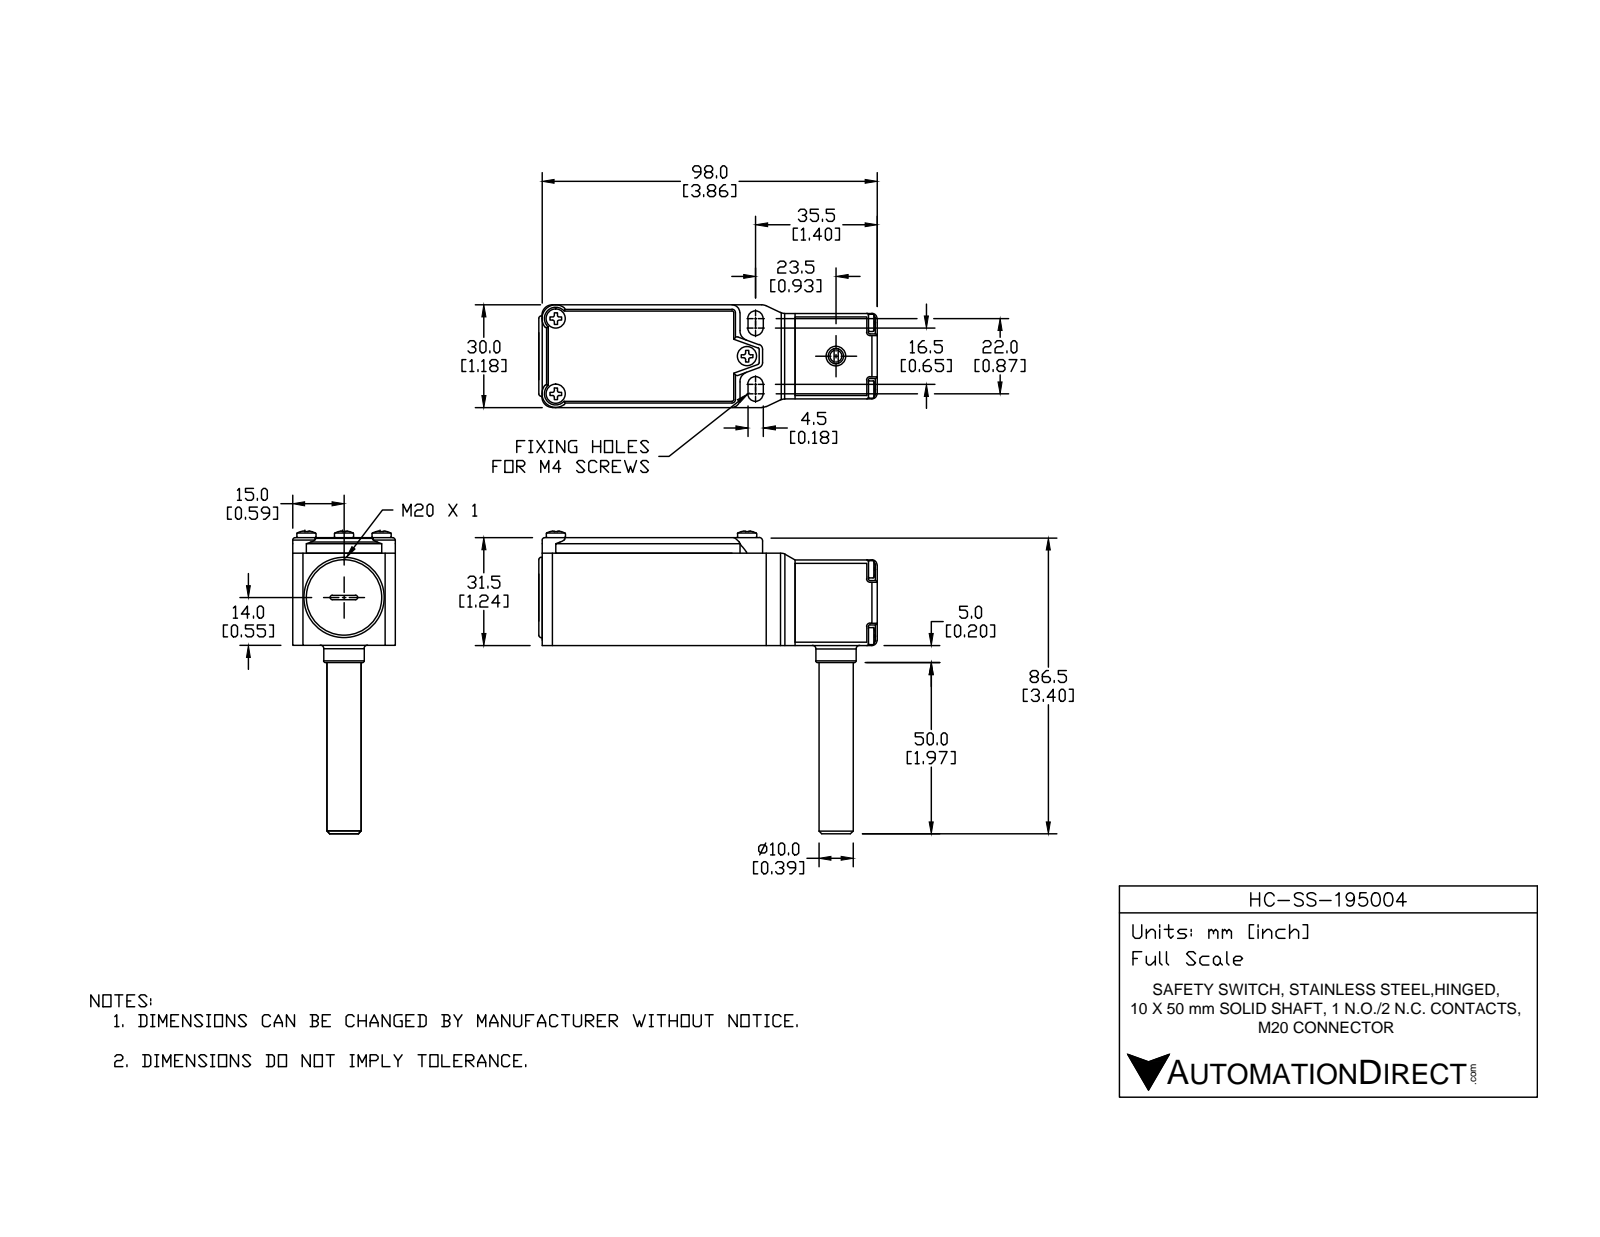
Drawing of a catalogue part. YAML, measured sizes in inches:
part_name: "HC-SS-195004"
step_written_by: "SolidWorks 2014 (AUTOMOTIVE_DESIGN)"
units: inches
bodies: {solids: 13, faces: 1168, planar: 347, cylindrical: 466, other: 355}
overall_size: [3.898, 3.482, 1.181]
volume: 2.649
surface_area: 52.99
round_holes:
  - {diameter: 0.098, count: 8}
  - {diameter: 0.126, count: 7}
  - {diameter: 0.157, count: 3}
  - {diameter: 0.059, count: 2}
  - {diameter: 0.071, count: 2}
  - {diameter: 0.087, count: 2}
  - {diameter: 0.142, count: 2}
  - {diameter: 0.081, count: 1}
  - {diameter: 0.114, count: 1}
  - {diameter: 0.173, count: 1}
  - {diameter: 0.185, count: 1}
  - {diameter: 0.217, count: 1}
round_bosses_or_shafts:
  - {diameter: 0.118, count: 7}
  - {diameter: 0.197, count: 5}
  - {diameter: 0.138, count: 4}
  - {diameter: 0.22, count: 3}
  - {diameter: 0.925, count: 1}
  - {diameter: 0.697, count: 1}
  - {diameter: 0.394, count: 1}
  - {diameter: 0.386, count: 1}
partial_cylinders:
  - {radius: 0.02, count: 175}
  - {radius: 0.039, count: 20}
  - {radius: 0.012, count: 18}
  - {radius: 0.006, count: 14}
  - {radius: 0.028, count: 8}
  - {radius: 0.118, count: 8}
  - {radius: 0.059, count: 6}
  - {radius: 0.089, count: 4}
face_to_face_distances: [0.098, 1.142, 0.079, 0.114, 1.067, 1.181, 0.177, 1.24, 0.016, 1.083]
hole_center_spacings: [0.543, 0.768, 0.187, 0.245, 0.414, 0.423, 0.426, 0.476]
